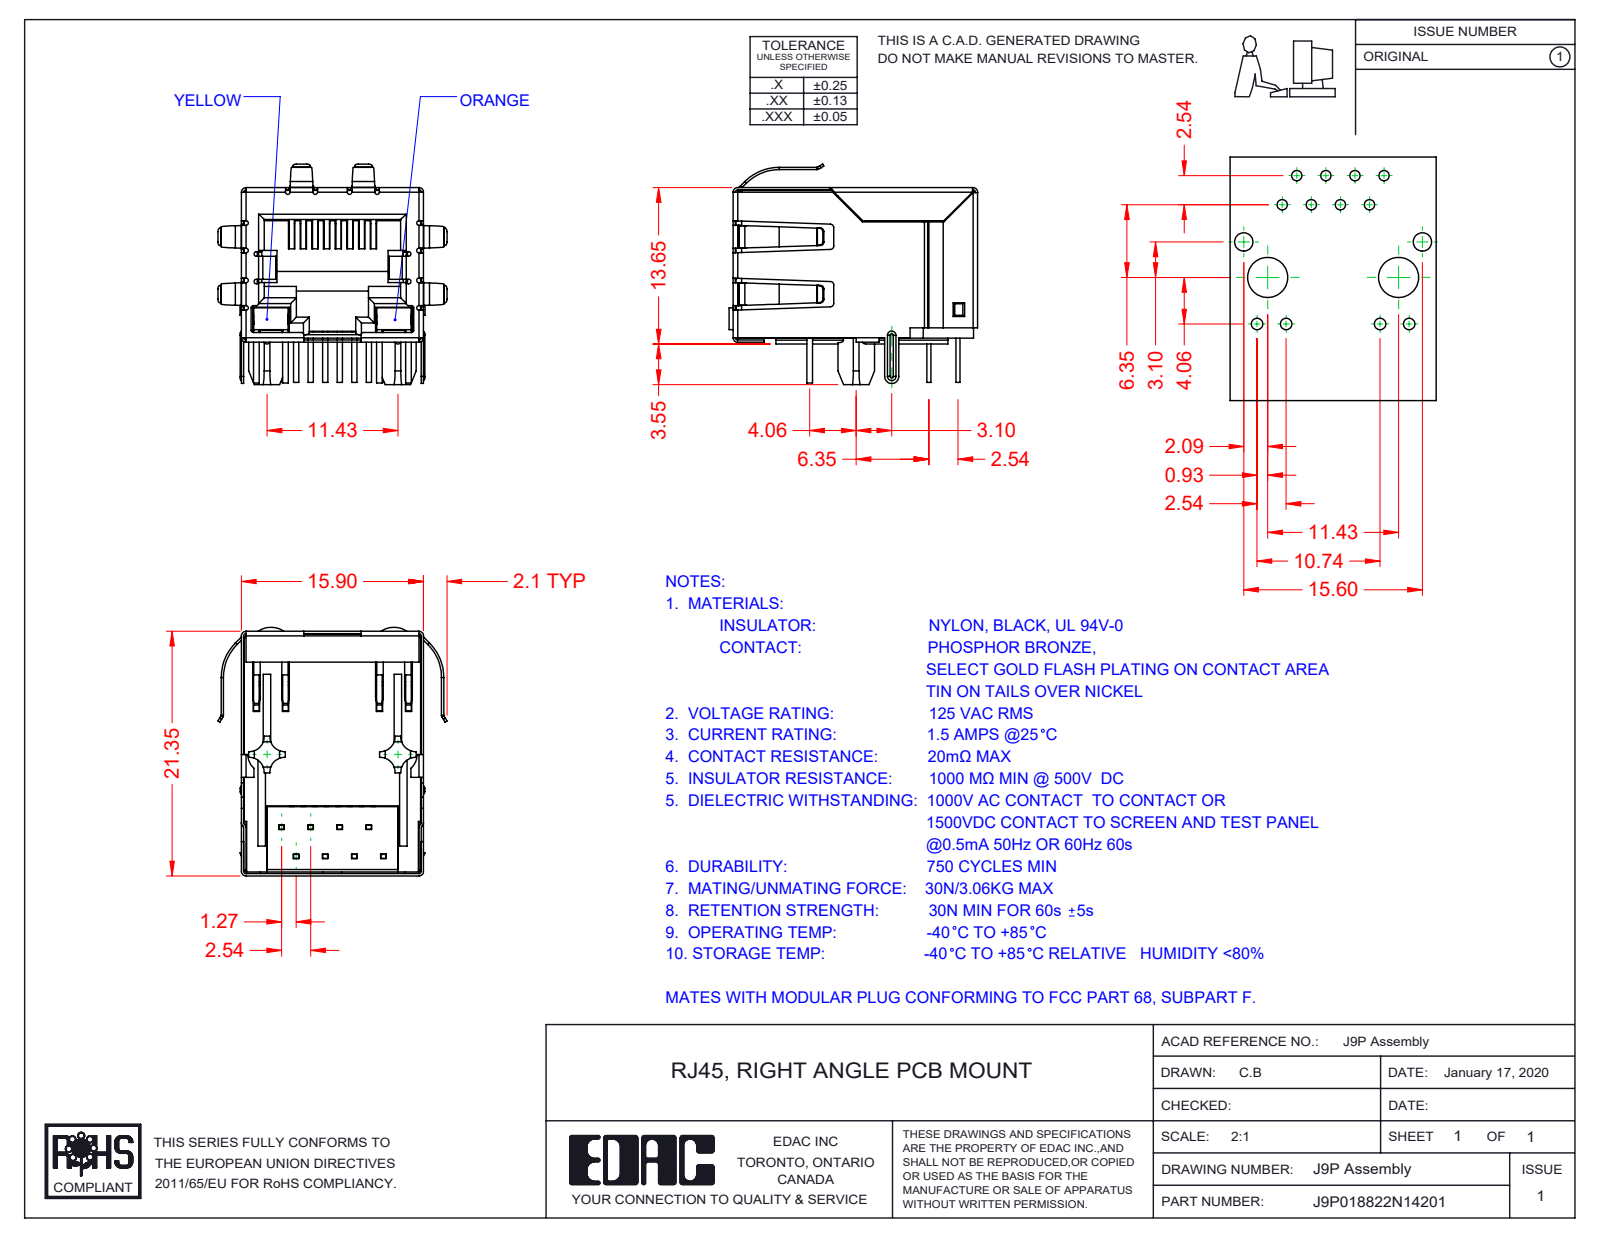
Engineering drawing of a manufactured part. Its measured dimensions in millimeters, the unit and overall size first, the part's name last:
Units: millimetres
Overall size (bounding box): 21.7 × 20 × 19.25
Partial cylindrical surfaces — rounded edges, fillets, slot ends (radius × count): R0.2 ×39, R0.5 ×22, R0.3 ×20, R0.4 ×16, R1.3 ×8, R0.23 ×5, R0.11 ×4, R0.31 ×4
Main face-to-face distances: 15.45, 15.7, 15.65, 0.35, 0.54, 15.5, 12.36, 0.6, 1.4, 0.59
Volume: 2 687 mm³ · Surface area: 7 515 mm²
Bodies: 13 solids, 1472 faces (1042 planar, 336 cylindrical, 94 other)
Part name (STEP PRODUCT): 9P-LED LED LH_1-Yellow; 9P-LED Contacts; 9P-LED Shield; 9P-LED Insulator (+4 more)
STEP written by: SolidWorks 2016 (CONFIG_CONTROL_DESIGN)
